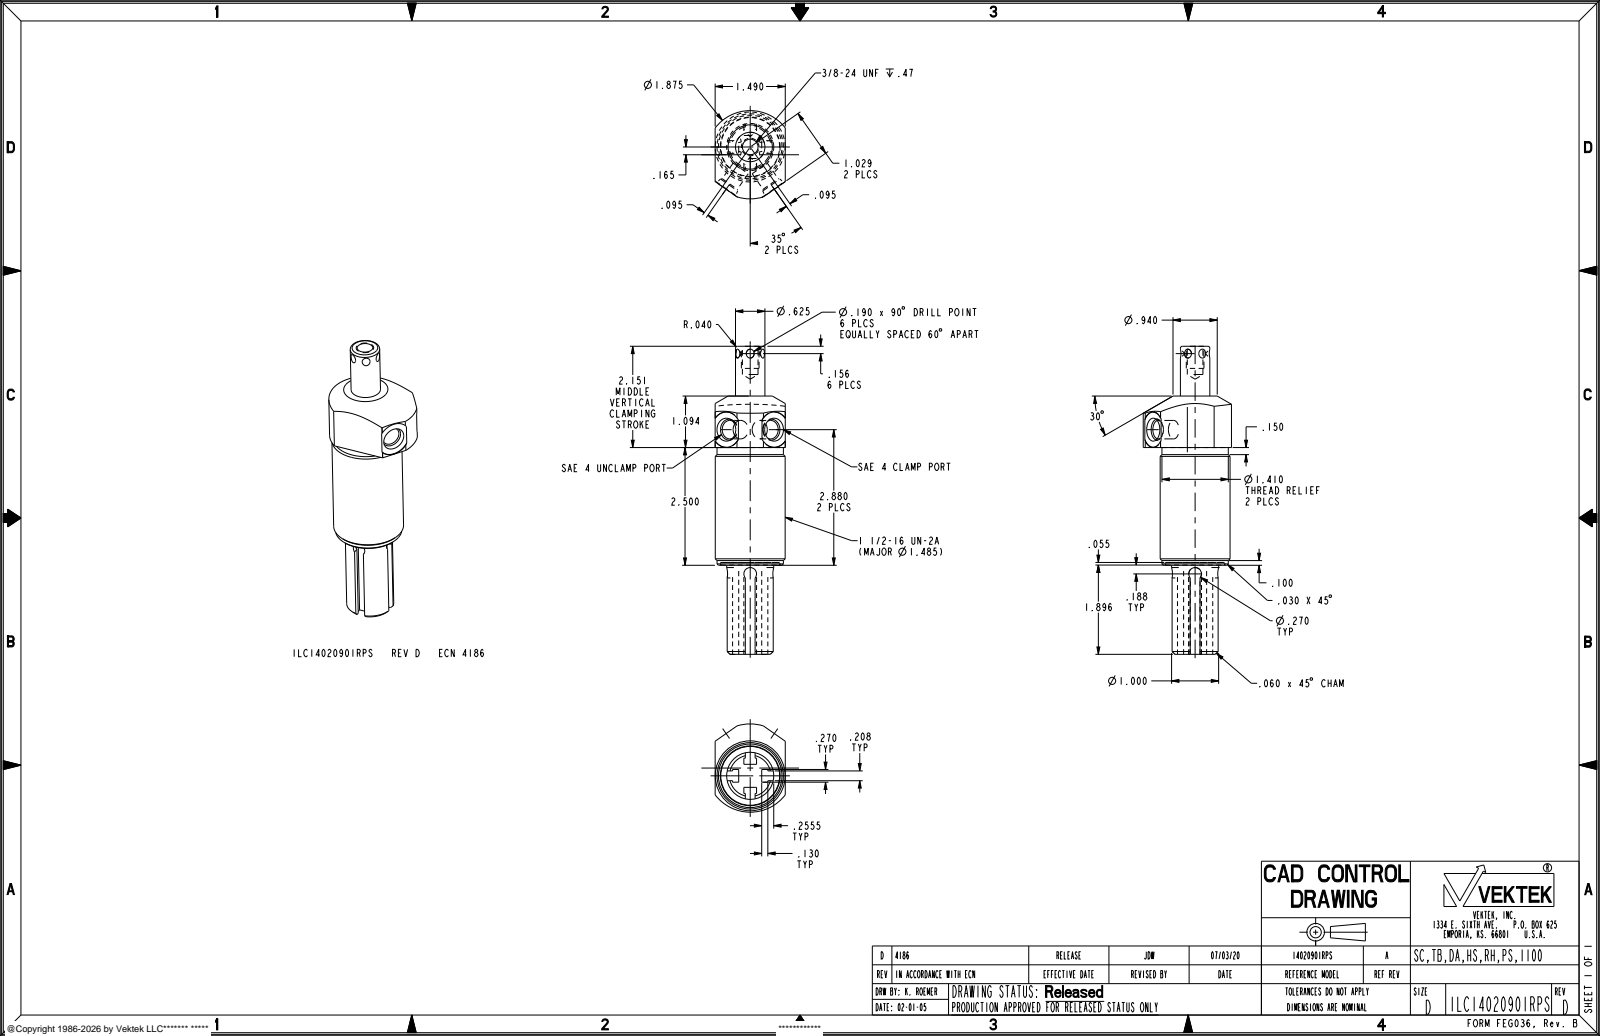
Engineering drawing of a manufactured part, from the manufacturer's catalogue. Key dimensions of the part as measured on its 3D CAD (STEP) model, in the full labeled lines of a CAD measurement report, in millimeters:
Part name (STEP PRODUCT): ILC14020901RPS
STEP written by: PRO/ENGINEER BY PARAMETRIC TECHNOLOGY CORPORATION, 2013320 (AUTOMOTIVE_DESIGN)
Units: millimetres
Bodies: 1 solid, 118 faces (46 planar, 36 cylindrical, 36 other)
Overall size (bounding box): 166.2 × 47.6 × 37.8
Volume: 128 400 mm³ · Surface area: 23 790 mm²
Round holes (diameter × count): ⌀10 ×2, ⌀8.4 ×1, ⌀32.3 ×1
Round bosses / shafts (diameter × count): ⌀37.7 ×1, ⌀35.8 ×1, ⌀31.8 ×1, ⌀25.4 ×1, ⌀15.9 ×1, ⌀9.5 ×1
Partial cylindrical surfaces — rounded edges, fillets, slot ends (radius × count): R3.4 ×2, R9.5 ×2, R23.8 ×1
Main face-to-face distances: 2.8, 9.7, 3.6, 8.8, 0.8, 6.1, 37.8, 12.7, 25.1, 12.4
